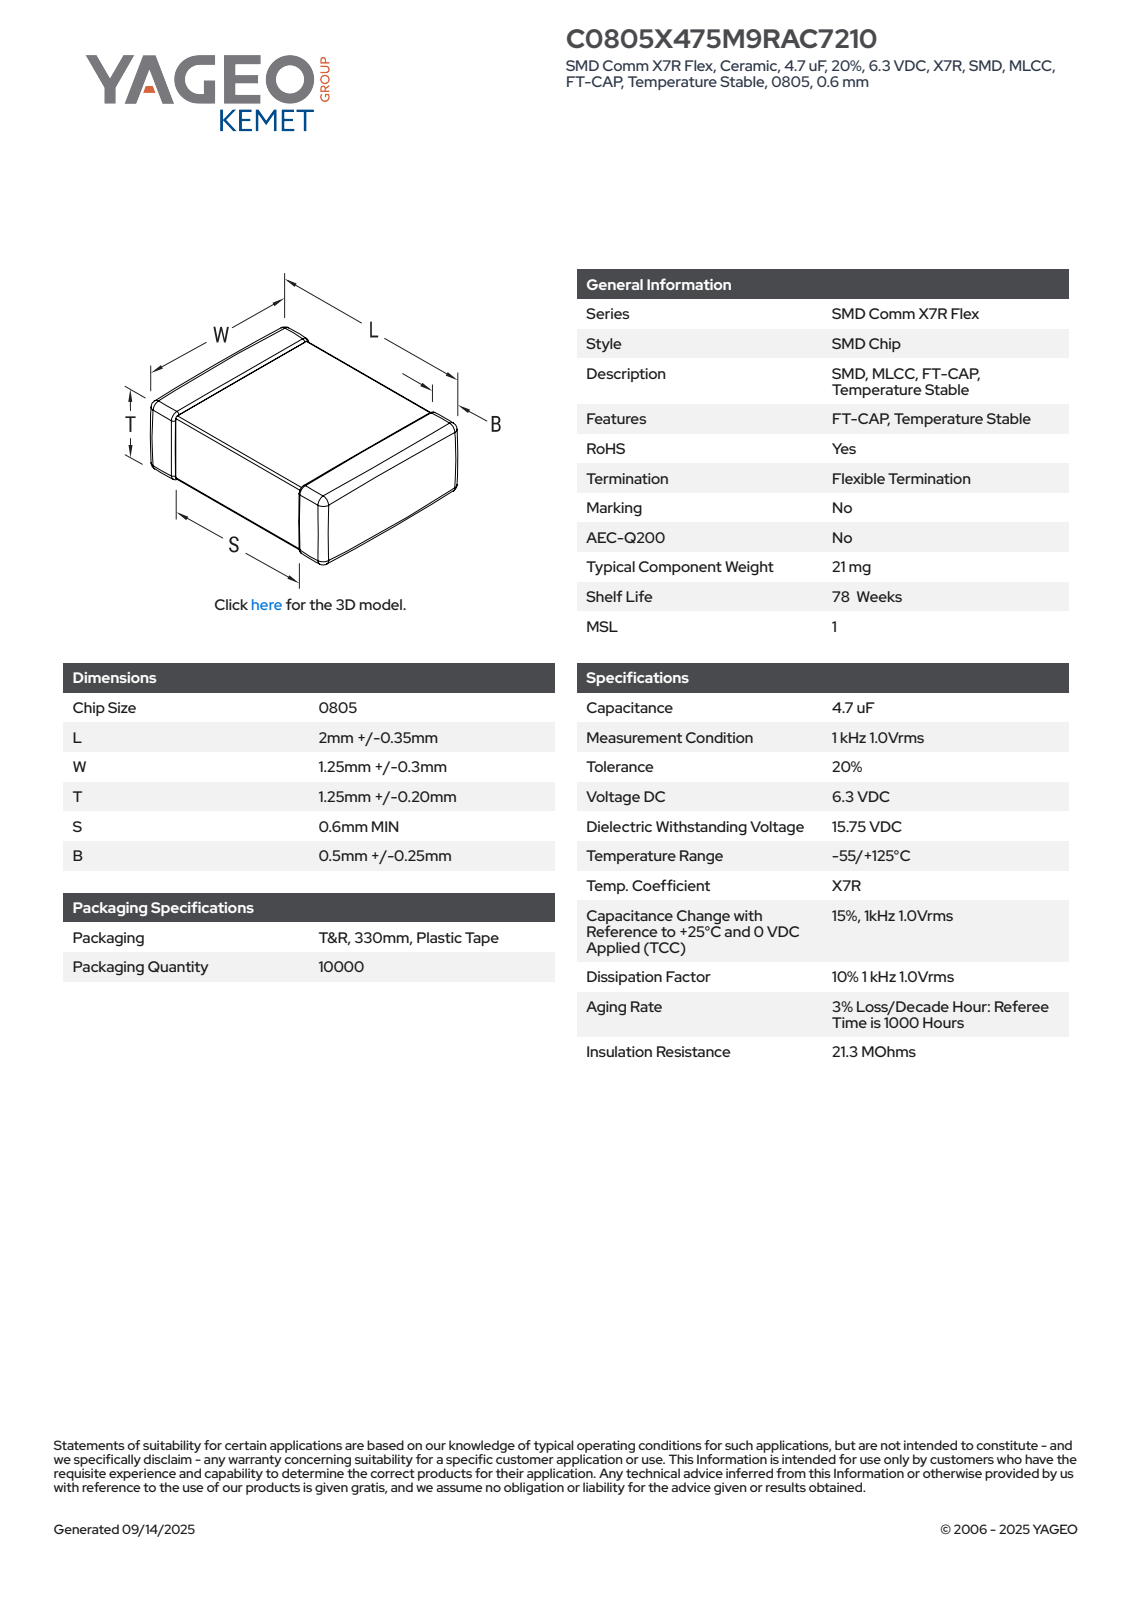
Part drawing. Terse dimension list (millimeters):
name: CCS_CCSTD_0805_L2.35W1.55T1.45B0.5
written by: SolidWorks 2014 (AUTOMOTIVE_DESIGN)
unit: mm
bodies: 4 solids, 125 faces (71 planar, 38 cylindrical, 16 other)
size: 2.35 × 1.55 × 1.45
volume: 5 mm³; area: 18 mm²
face distances: 1.42, 1.52, 2.35, 1.39, 1.49, 1.45, 1.55, 1.04, 1.31, 1.08
